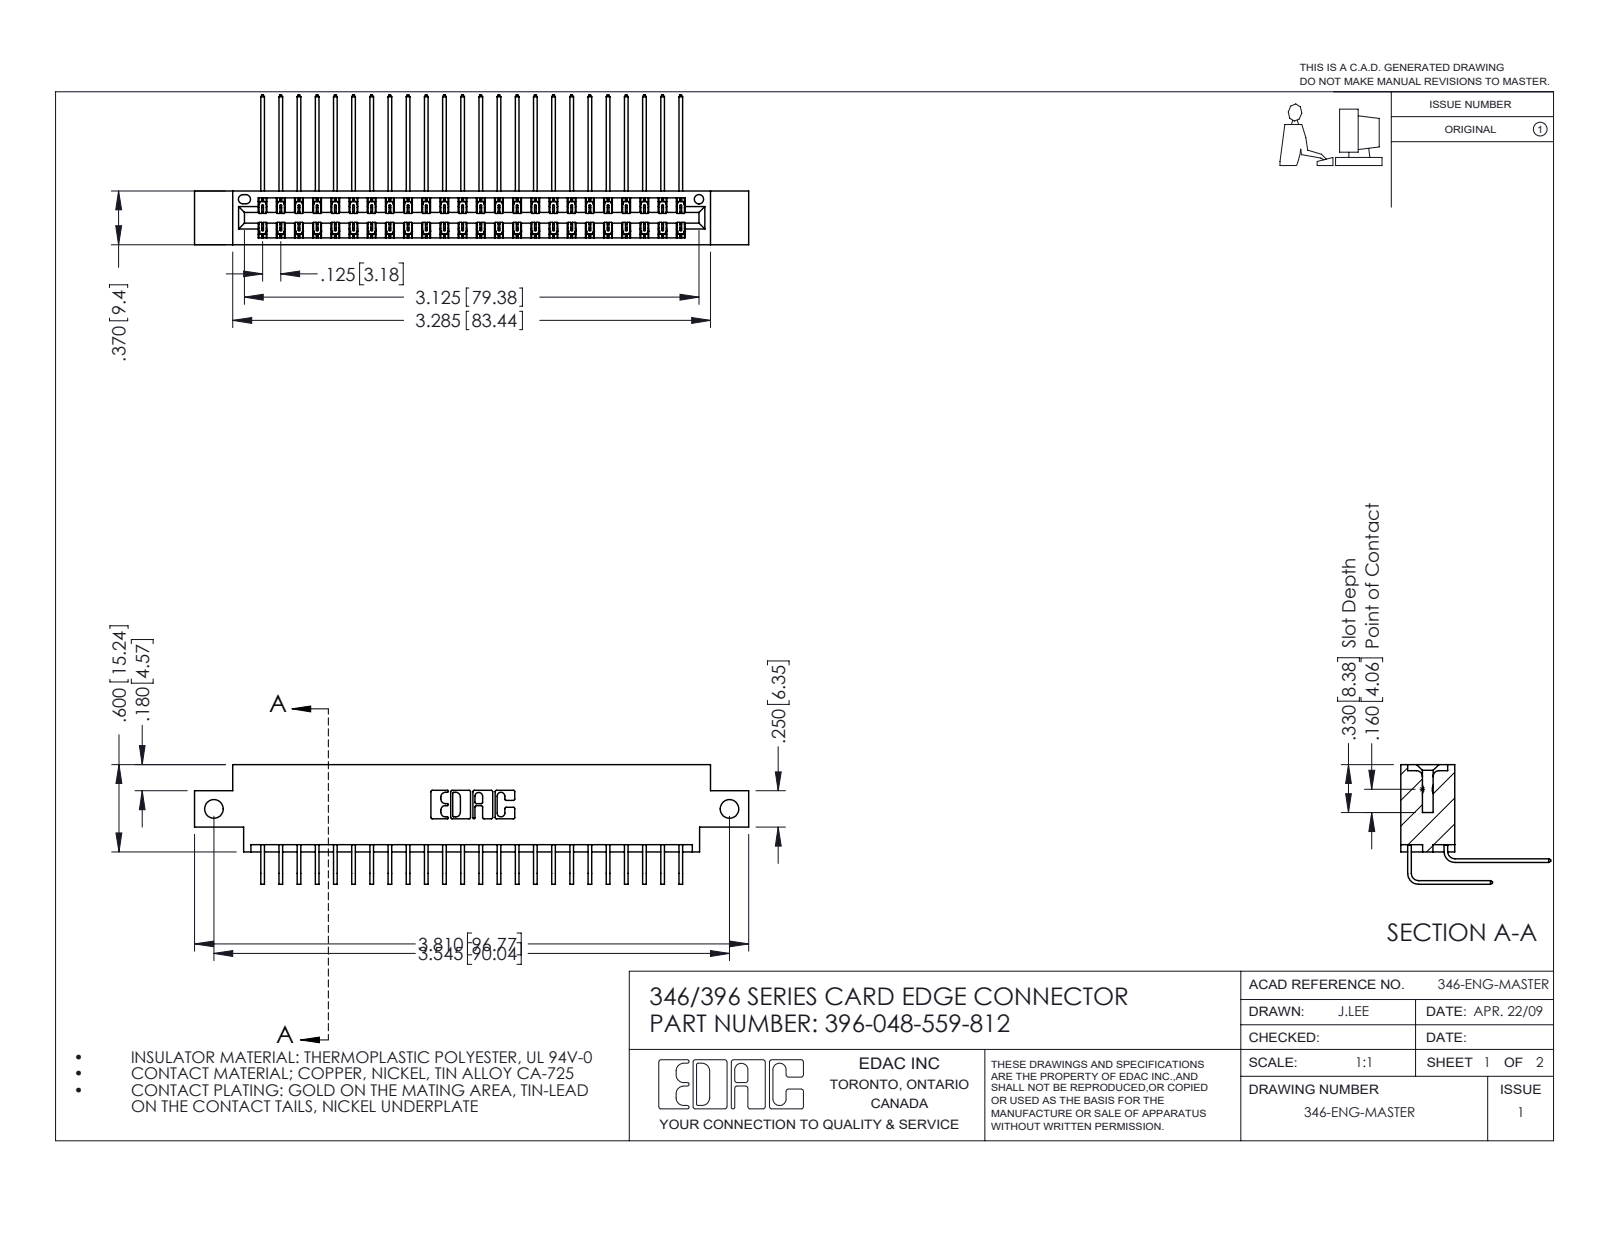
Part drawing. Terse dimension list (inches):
name: 346 Part_0.170 Offset - Side Mount; 396-048-559-812; 345-292-001_559 Tail - 2; 345-292-001_558 559 Tail - 1
written by: SolidWorks 2016 (CONFIG_CONTROL_DESIGN)
unit: in
bodies: 49 solids, 2718 faces (1856 planar, 862 cylindrical, 0 other)
size: 3.81 × 1.03 × 0.823
volume: 0.569 in³; area: 21.57 in²
holes: 2× ⌀0.128, 1× ⌀0.064
rounds: 72× R0.006, 22× R0.01, 6× R0.007, 6× R0.031, 3× R0.026, 2× R0.014, 2× R0.022, 2× R0.024
face distances: 0.048, 0.322, 0.37, 0.025, 0.25, 0.072, 0.298, 0.275, 0.15, 0.148
hole spacings: 3.545
